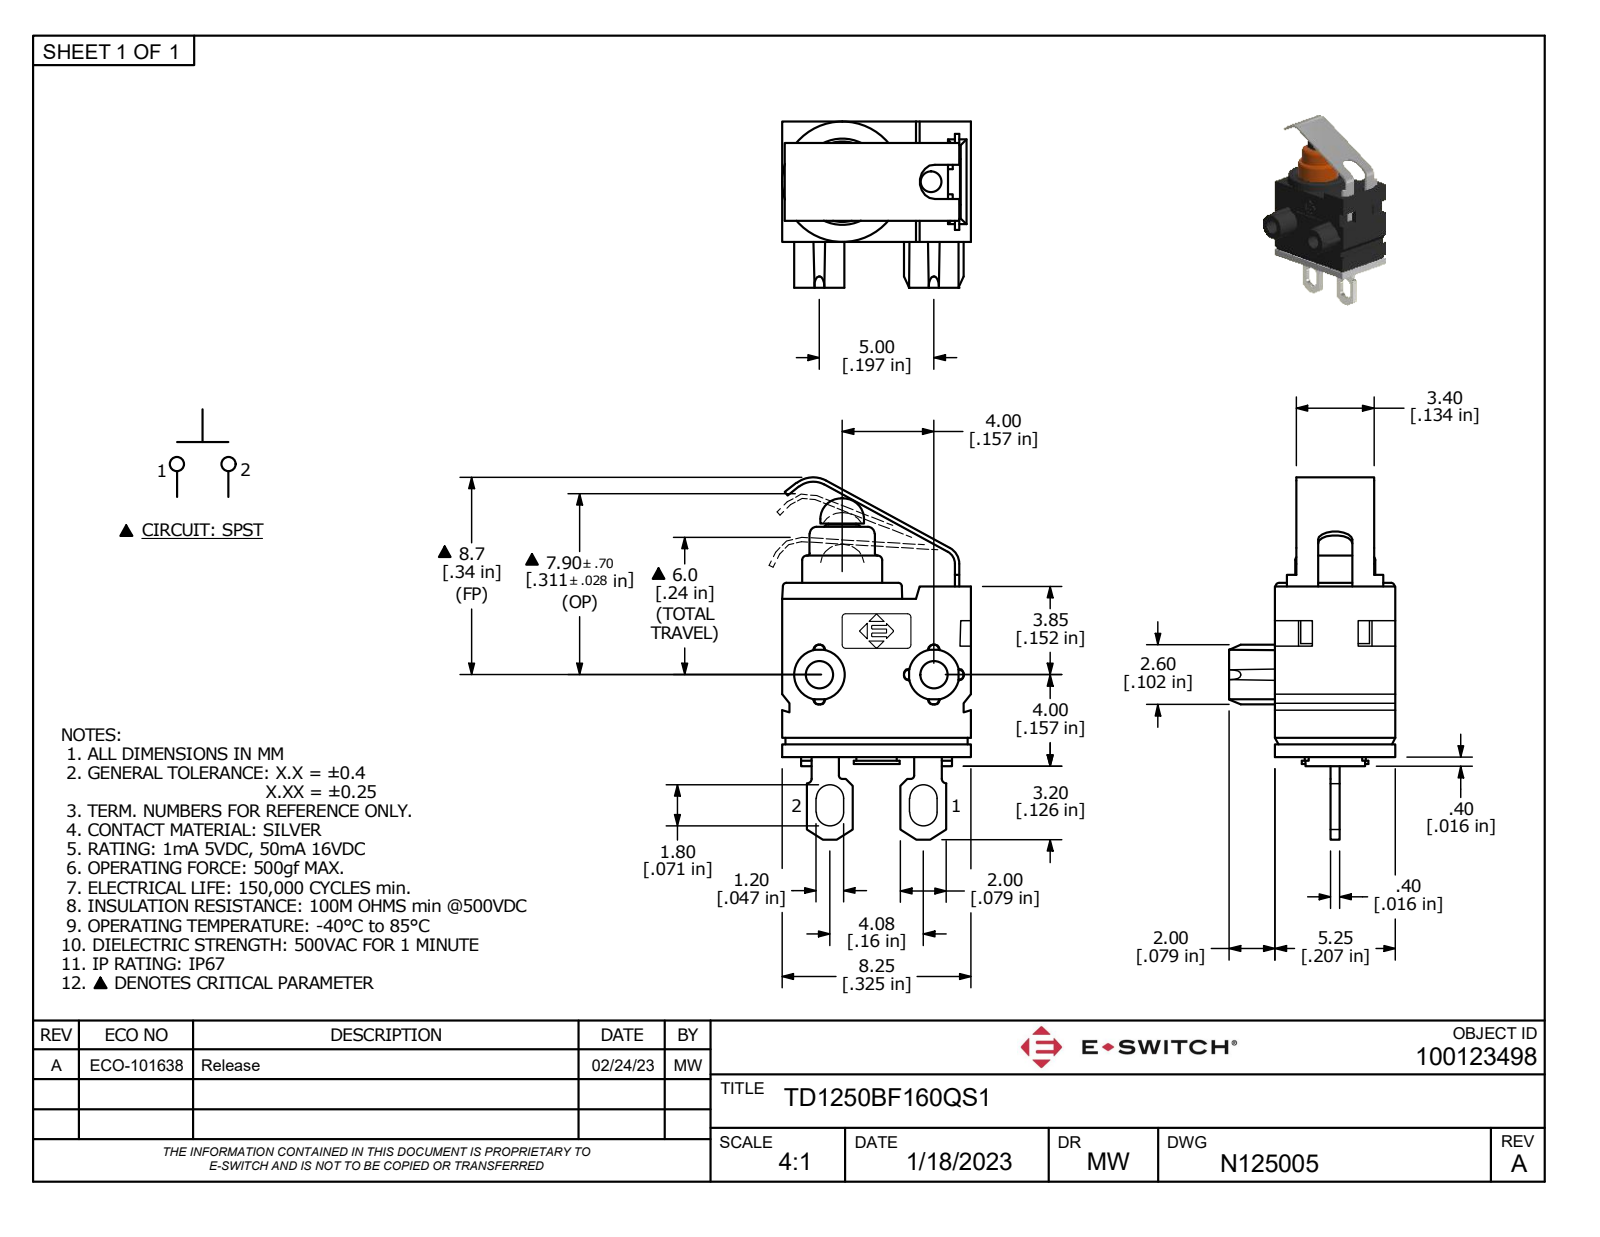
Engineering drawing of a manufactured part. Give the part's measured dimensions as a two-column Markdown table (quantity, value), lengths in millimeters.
| quantity | value |
| --- | --- |
| part name | TD1250BF160QS1 |
| STEP written by | Autodesk Inventor 2022 (AUTOMOTIVE_DESIGN) |
| units | millimeters |
| bodies | 1 solid, 298 faces (228 planar, 58 cylindrical, 12 other) |
| overall size | 15.82 × 8.25 × 7.25 |
| volume | 356 mm³ |
| surface area | 532 mm² |
| round holes (diameter × count) | 1.2 × 2, 4.65 × 1 |
| round bosses / shafts (diameter × count) | 4.5 × 1, 3.5 × 1, 2.85 × 1, 2.2 × 1, 1.9 × 1, 1.2 × 1 |
| partial cylindrical surfaces (radius × count) | 0.2 × 14, 0.15 × 8, 0.6 × 5, 0.1 × 3, 0.75 × 1, 0.79 × 1, 1 × 1, 1.1 × 1 |
| main face-to-face distances | 5.24, 8.24, 0.55, 2.42, 2.82, 6.9, 7.45, 0.5, 0.4, 7.24 |
| hole center spacings | 5 |
